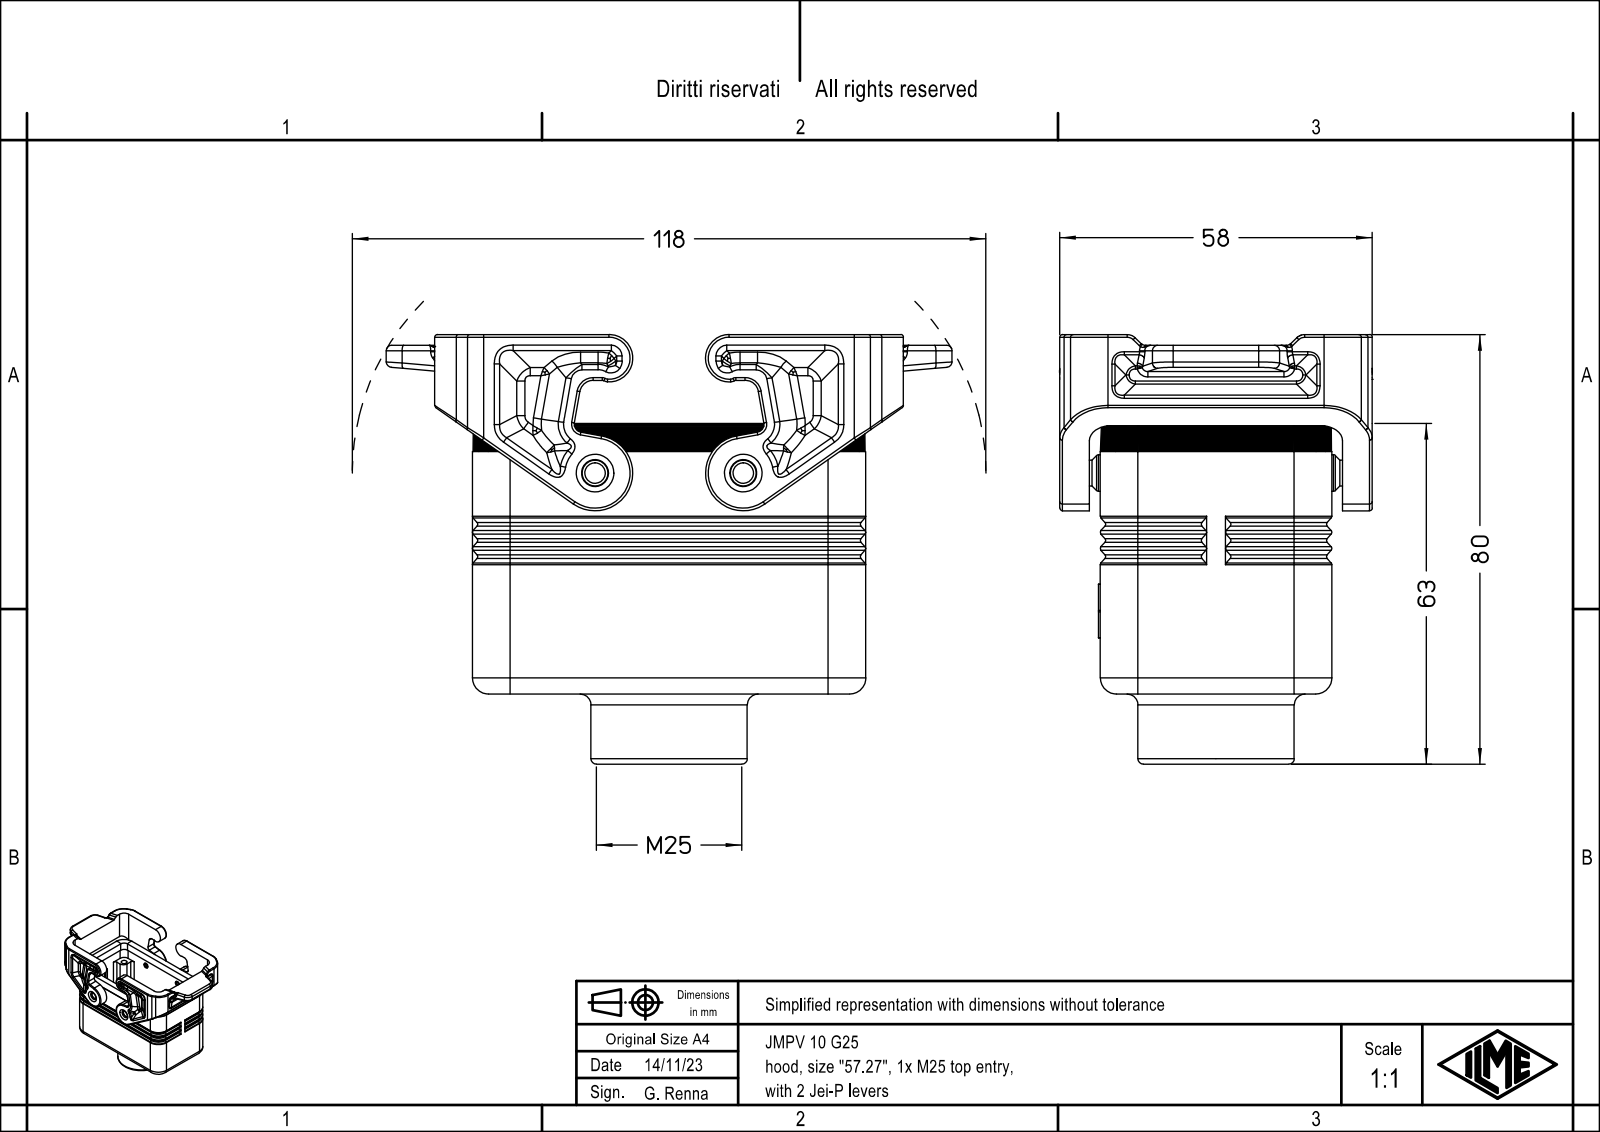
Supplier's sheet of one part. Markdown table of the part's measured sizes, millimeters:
| quantity | value |
| --- | --- |
| part name | JMPV 10 G25 |
| STEP written by | Creo Elements/Direct Modeling 20.1B 02-Apr-2019 (C) Parametric Technology GmbH (AUTOMOTIVE_DESIGN) |
| units | millimeters |
| bodies | 1 solid, 1014 faces (233 planar, 355 cylindrical, 426 other) |
| overall size | 105 × 79.7 × 58.08 |
| volume | 75 519 mm³ |
| surface area | 42 217 mm² |
| round holes (diameter × count) | 3 × 4, 3.5 × 4, 4.8 × 2, 19 × 1, 23.6 × 1 |
| round bosses / shafts (diameter × count) | 6.8 × 2, 29 × 1 |
| partial cylindrical surfaces (radius × count) | 0.5 × 78, 3 × 34, 1 × 32, 1.5 × 26, 2 × 20, 0.33 × 15, 4 × 12, 6 × 12 |
| main face-to-face distances | 3.5, 2, 5.5, 39.5, 45, 41.5, 47, 36, 43, 2.8 |
| hole center spacings | 31.54, 27, 57, 63.07, 27.5 |
